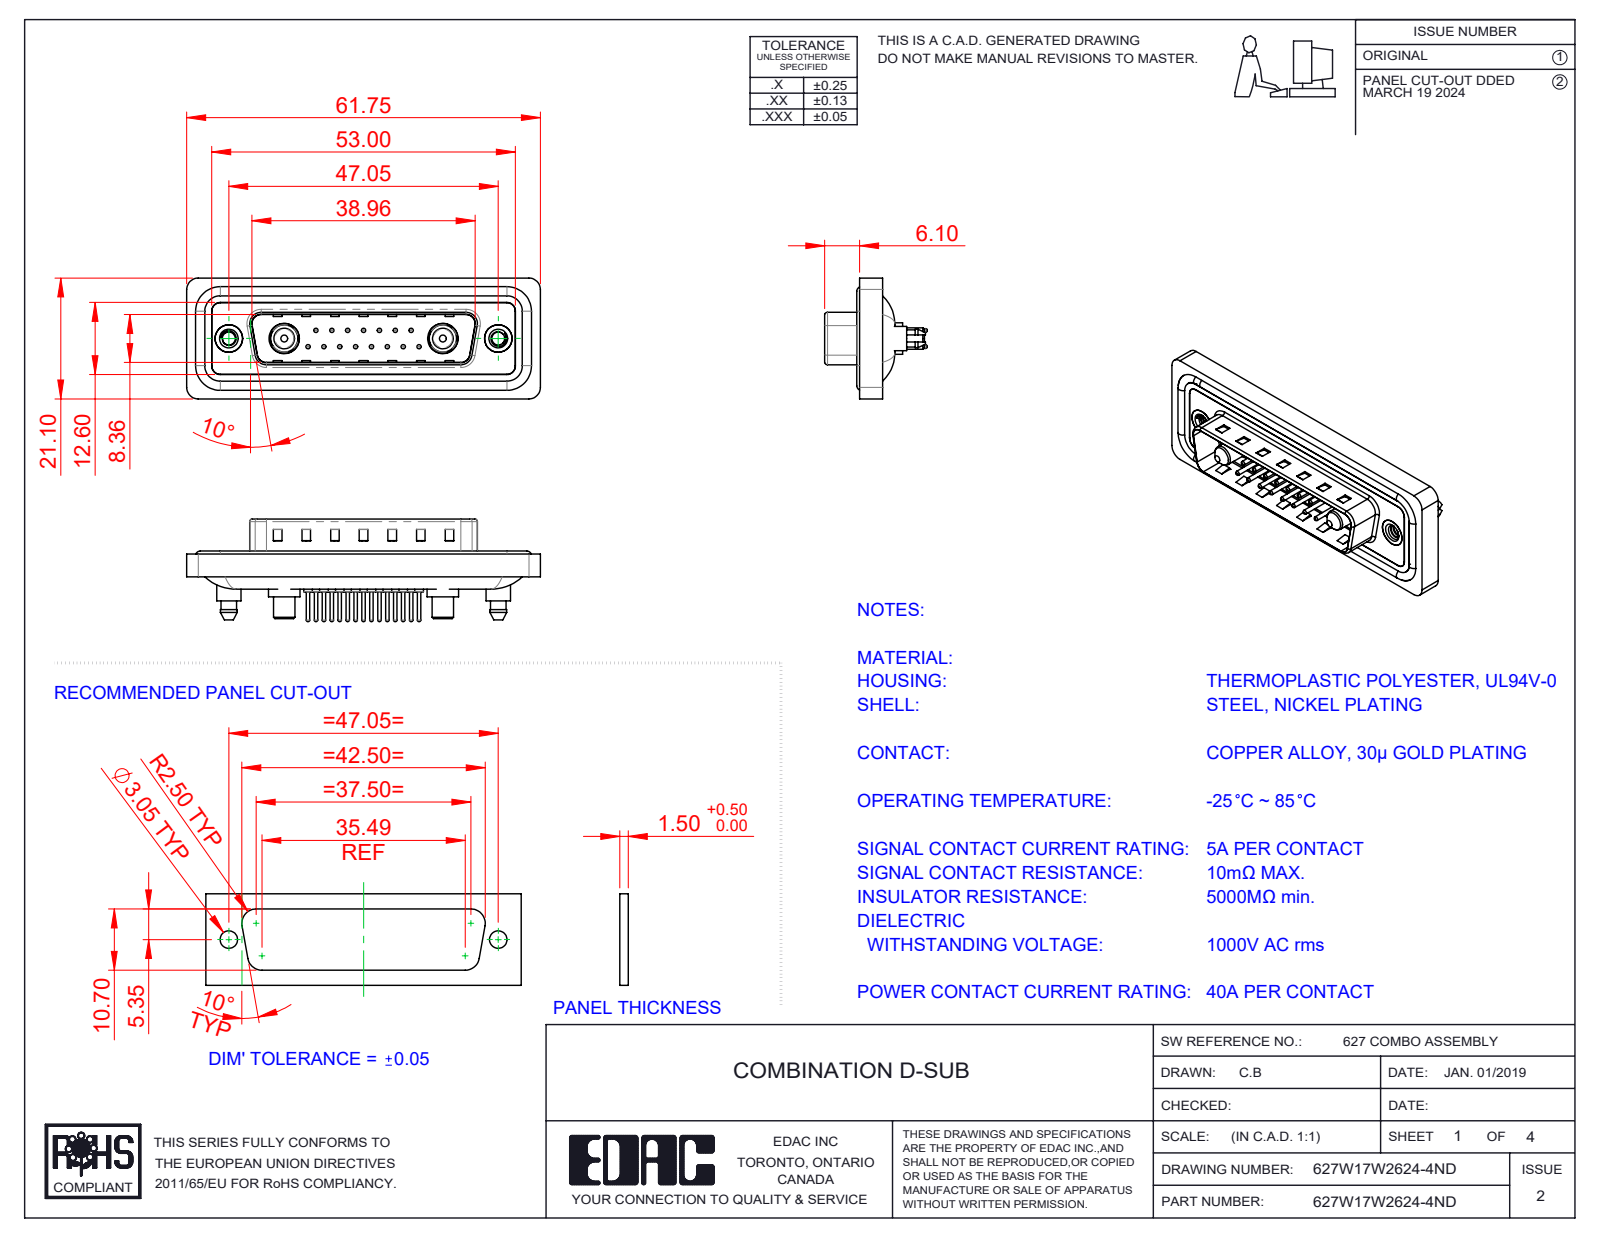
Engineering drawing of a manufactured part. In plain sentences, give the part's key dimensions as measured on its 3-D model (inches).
The part is named "627Combo Contact Row 2_24; 627W17W2624-4ND; 627Combo Housing_17W2; 627Combo Shell Rear_25 Contacts (+6 more)". Its 3-D file was written by "SolidWorks 2023 (CONFIG_CONTROL_DESIGN)". It is 26 solids with 1174 faces: 350 planar, 476 cylindrical and 348 other. Overall it measures 2.431 by 0.831 by 0.705 inches. Its volume is 0.454 cubic inches and its surface area 19.02 square inches. Round holes: 15 of diameter 0.03, 15 of diameter 0.063, 15 of diameter 0.079, 2 of diameter 0.089, 2 of diameter 0.157, 2 of diameter 0.189, 2 of diameter 0.191, 2 of diameter 0.197, 2 of diameter 0.209. Round bosses or shafts: 15 of diameter 0.059, 15 of diameter 0.024, 4 of diameter 0.063, 2 of diameter 0.217, 2 of diameter 0.213, 2 of diameter 0.205, 2 of diameter 0.193, 2 of diameter 0.187. Partial cylindrical surfaces (rounded edges, fillets, slot ends): 24 of radius 0.059, 18 of radius 0.079, 10 of radius 0.063, 8 of radius 0.02, 4 of radius 0.01, 4 of radius 0.024, 4 of radius 0.026, 4 of radius 0.035. The main face-to-face distances are 0.016, 0.059, 0.043, 0.063, 0.02, 0.122, 0.114, 0.032, 0.377, 0.161. The hole center spacings are 0.124, 0.109, 0.218, 0.327, 0.198, 0.295, 0.436, 0.198.
